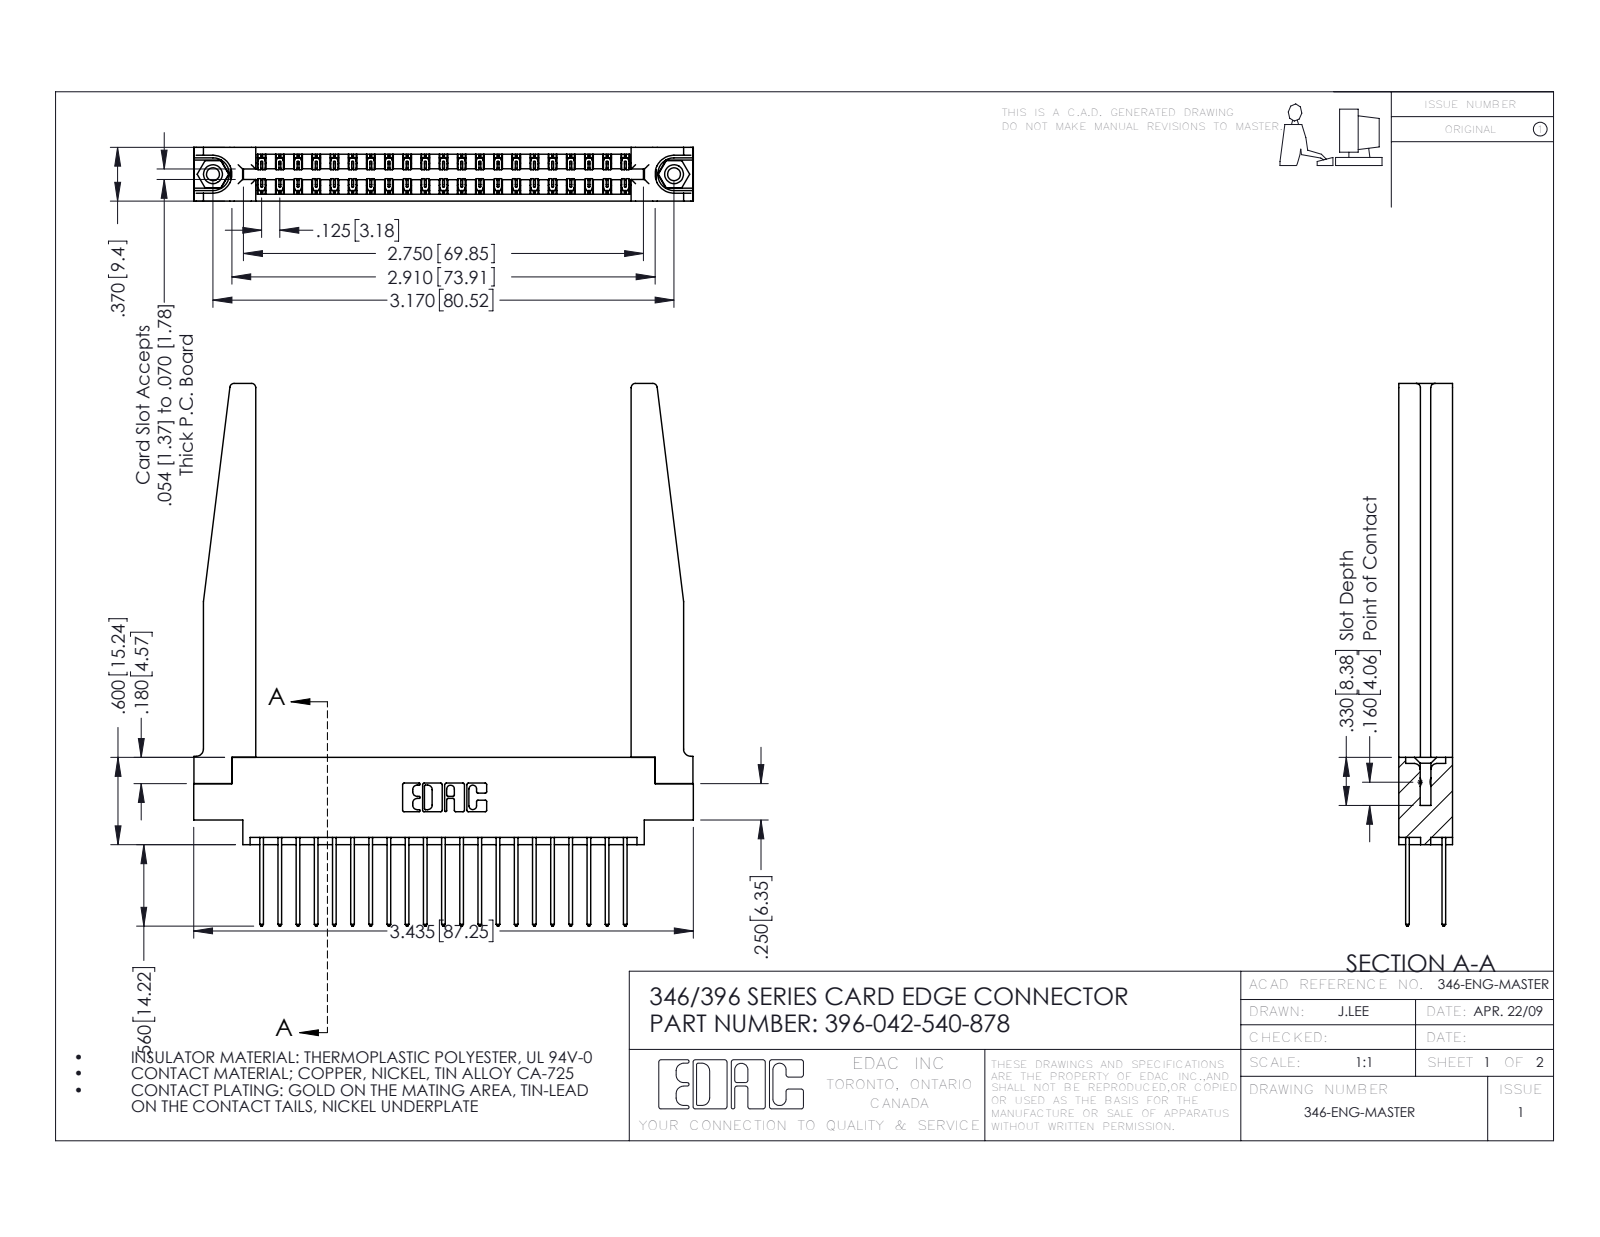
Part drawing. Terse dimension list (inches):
name: 346 Part_0.170 Offset - 0.156 Dia-TH; 346-220-078_345-220-078; 396-042-540-878; 345-250-001_345-250-001-102 (+1 more)
written by: SolidWorks 2016 (CONFIG_CONTROL_DESIGN)
unit: in
bodies: 47 solids, 2544 faces (1692 planar, 800 cylindrical, 52 other)
size: 3.73 × 3.435 × 0.37
volume: 0.931 in³; area: 28.86 in²
holes: 2× ⌀0.089, 2× ⌀0.125, 2× ⌀0.156, 1× ⌀0.064
bosses: 2× ⌀0.155
rounds: 63× R0.006, 42× R0.01, 22× R0.01, 8× R0.03, 6× R0.007, 6× R0.031, 3× R0.026, 2× R0.014
face distances: 0.37, 0.048, 0.322, 0.072, 0.25, 0.148, 0.15, 0.298, 0.025, 0.275
hole spacings: 0.246, 2.963, 3.17
